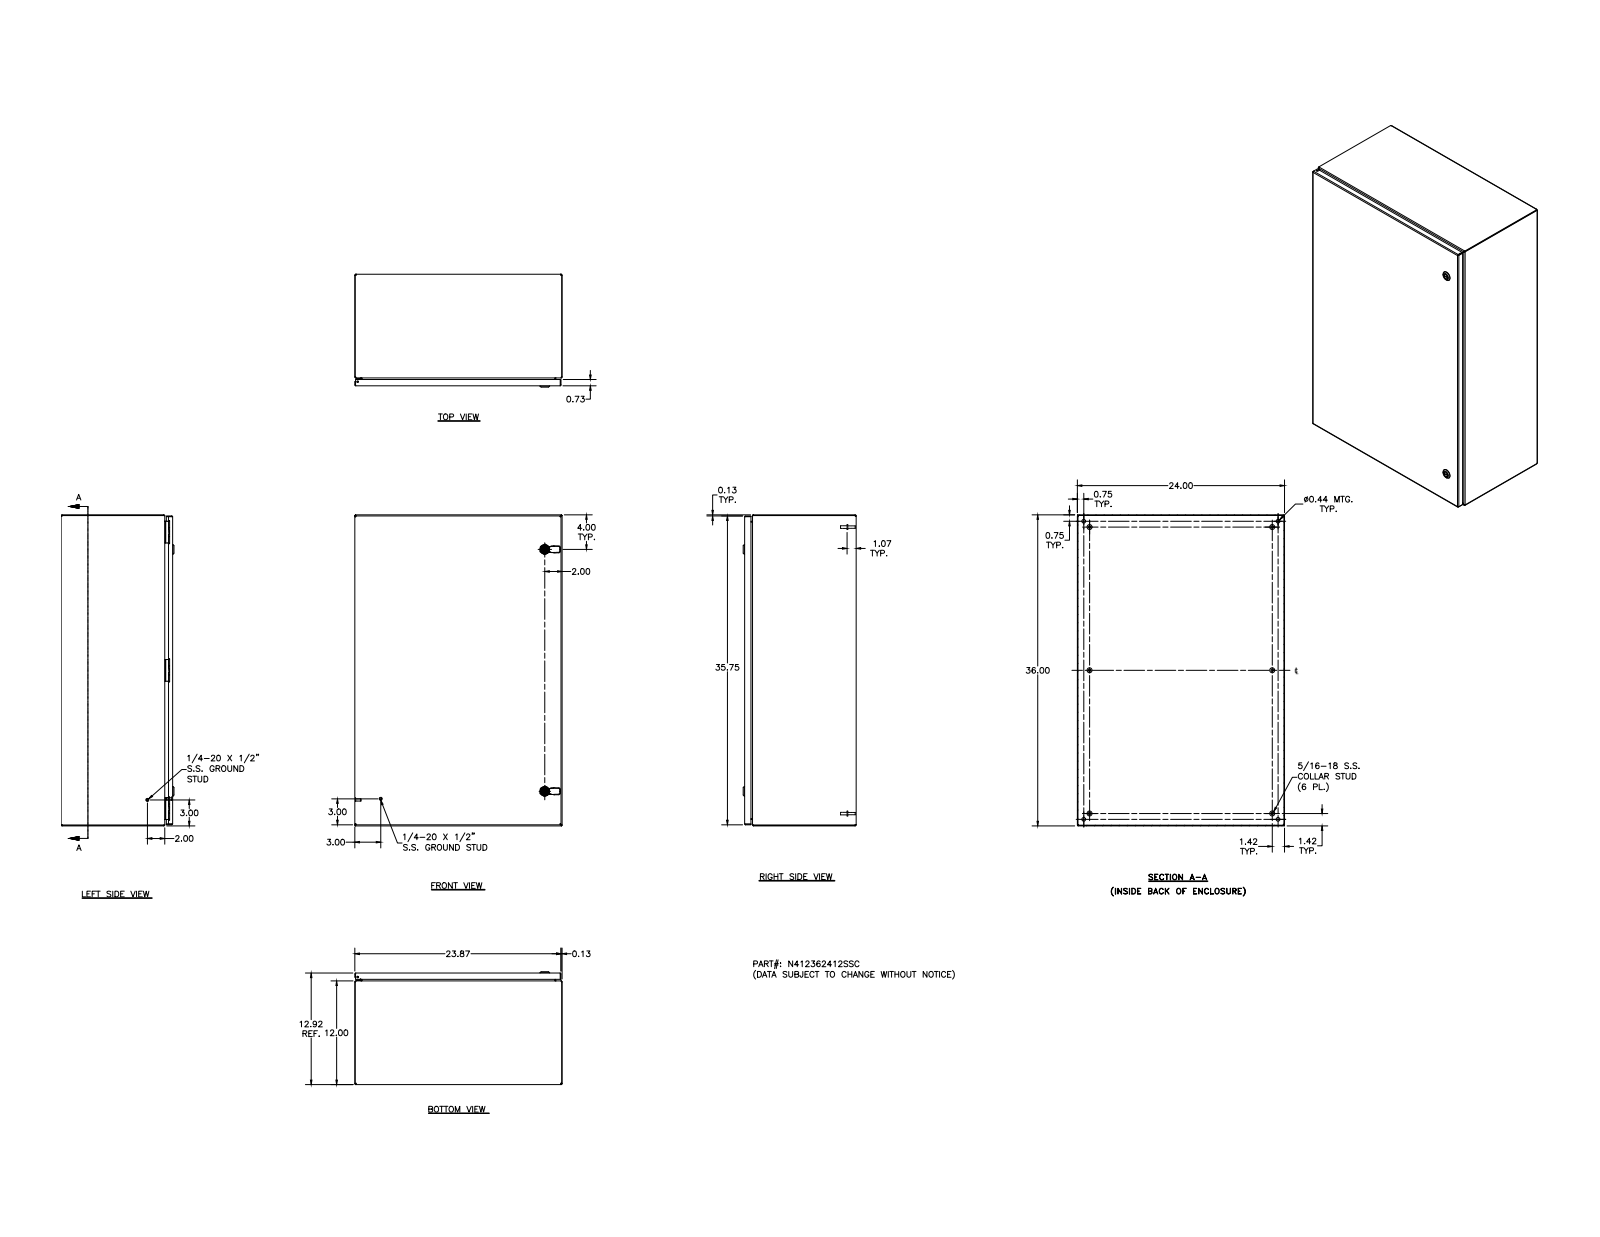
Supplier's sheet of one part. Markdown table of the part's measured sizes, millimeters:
| quantity | value |
| --- | --- |
| part name | N412362412SSC; N412362412SSCBKP; 388151; N4123624SSCLID (+8 more) |
| STEP written by | Autodesk Inventor 2011 (AUTOMOTIVE_DESIGN) |
| units | millimeters |
| bodies | 53 solids, 2118 faces (831 planar, 778 cylindrical, 509 other) |
| overall size | 914.4 × 609.6 × 332.1 |
| volume | 4 148 000 mm³ |
| surface area | 4 430 000 mm² |
| round holes (diameter × count) | 4.8 × 7, 2.4 × 6, 3.9 × 6, 4.2 × 6, 4.4 × 6, 11.1 × 4, 4 × 3, 5 × 2, 8 × 2, 10 × 2, 10.2 × 2, 16.1 × 2 |
| round bosses / shafts (diameter × count) | 6.4 × 14, 14.3 × 6, 9.1 × 6, 8.1 × 6, 7.6 × 6, 7 × 6, 6.5 × 6, 4.2 × 6 |
| partial cylindrical surfaces (radius × count) | 1.3 × 38, 0.8 × 34, 0.4 × 26, 3.2 × 21, 2.7 × 20, 0.5 × 15, 0.8 × 12, 1.8 × 8 |
| main face-to-face distances | 1.9, 326.2, 607.7, 324.3, 328.1, 912.5, 605.8, 609.6, 910.6, 914.4 |
| hole center spacings | 406.5, 812.8, 406.3, 0.4, 16.8, 406.2, 406.4, 406.6 |
